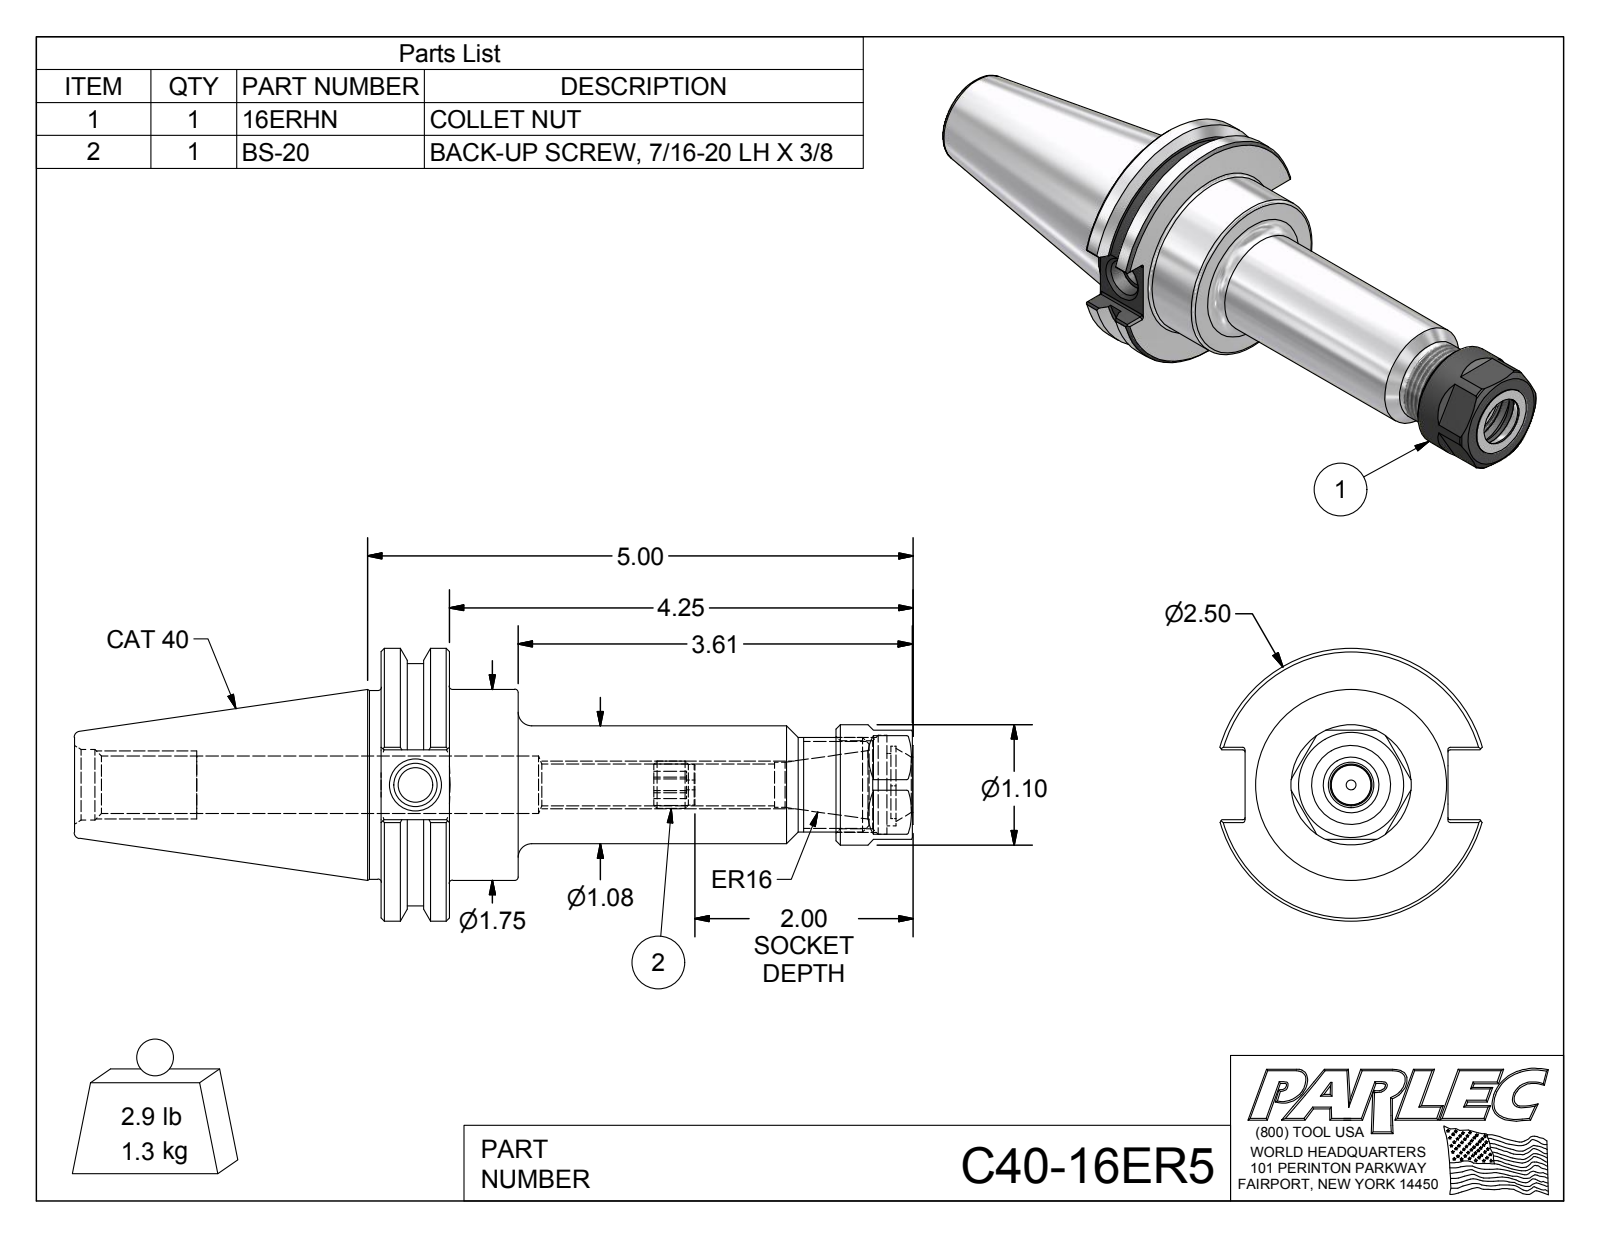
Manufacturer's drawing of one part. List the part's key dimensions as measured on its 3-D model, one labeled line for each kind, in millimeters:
Part name (STEP PRODUCT): C40-16ER5; C40-16ER5-1; BS-20; 16ERHN
STEP written by: Autodesk Inventor 2012 (AUTOMOTIVE_DESIGN)
Units: millimetres
Bodies: 3 solids, 138 faces (60 planar, 39 cylindrical, 39 other)
Overall size (bounding box): 195.3 × 63.5 × 61
Volume: 165 500 mm³ · Surface area: 36 420 mm²
Round holes (diameter × count): ⌀2.3 ×1, ⌀8 ×1, ⌀9.7 ×1, ⌀10.1 ×1, ⌀10.5 ×1, ⌀12.9 ×1, ⌀13.4 ×1, ⌀13.4 ×1, ⌀16.5 ×1, ⌀16.8 ×1, ⌀20.5 ×1, ⌀23 ×1
Round bosses / shafts (diameter × count): ⌀63.5 ×1, ⌀56.4 ×1, ⌀44.5 ×1, ⌀43.9 ×1, ⌀28 ×1, ⌀27.4 ×1, ⌀22 ×1, ⌀18.4 ×1
Partial cylindrical surfaces — rounded edges, fillets, slot ends (radius × count): R0.5 ×12, R9 ×1
Main face-to-face distances: 15.9, 31.9, 16, 107.8, 6, 25.4, 123.7, 91.8, 4.6, 20.8
Hole centre spacings: 1.3
